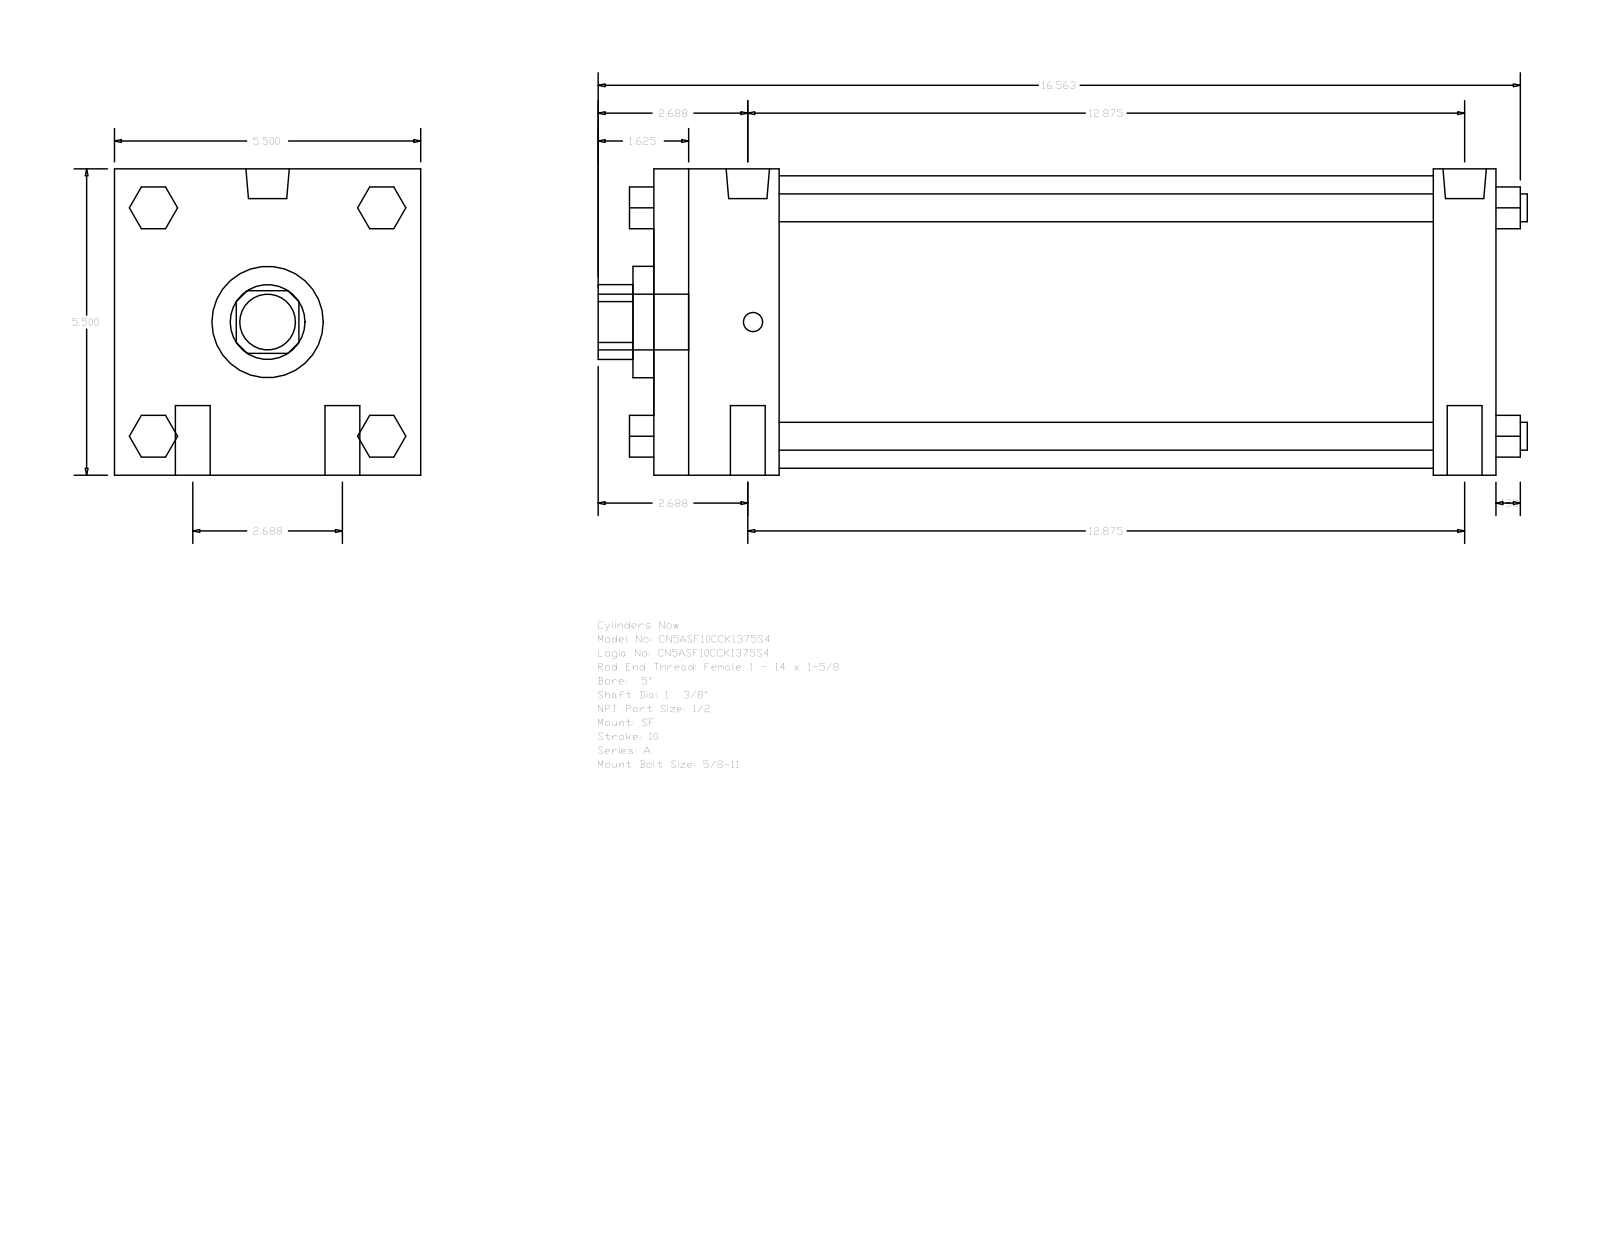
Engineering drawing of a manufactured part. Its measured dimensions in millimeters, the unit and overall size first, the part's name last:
Units: millimetres
Overall size (bounding box): 423.86 × 139.7 × 139.7
Round holes (diameter × count): ⌀34.92 ×1, ⌀50.8 ×1, ⌀133.35 ×1
Round bosses / shafts (diameter × count): ⌀15.88 ×4, ⌀12.7 ×4, ⌀19.77 ×2, ⌀8.73 ×2, ⌀25.4 ×1
Partial cylindrical surfaces — rounded edges, fillets, slot ends (radius × count): R17.06 ×1
Main face-to-face distances: 139.7, 384.17, 28.57, 57.15, 355.6, 298.45, 327.02, 19.05, 52.07, 90.18
Bodies: 0 solids, 124 faces (94 planar, 30 cylindrical, 0 other)
Part name (STEP PRODUCT): A_SF__0500_1.375
STEP written by: GSSL Pune (CONFIG_CONTROL_DESIGN)
